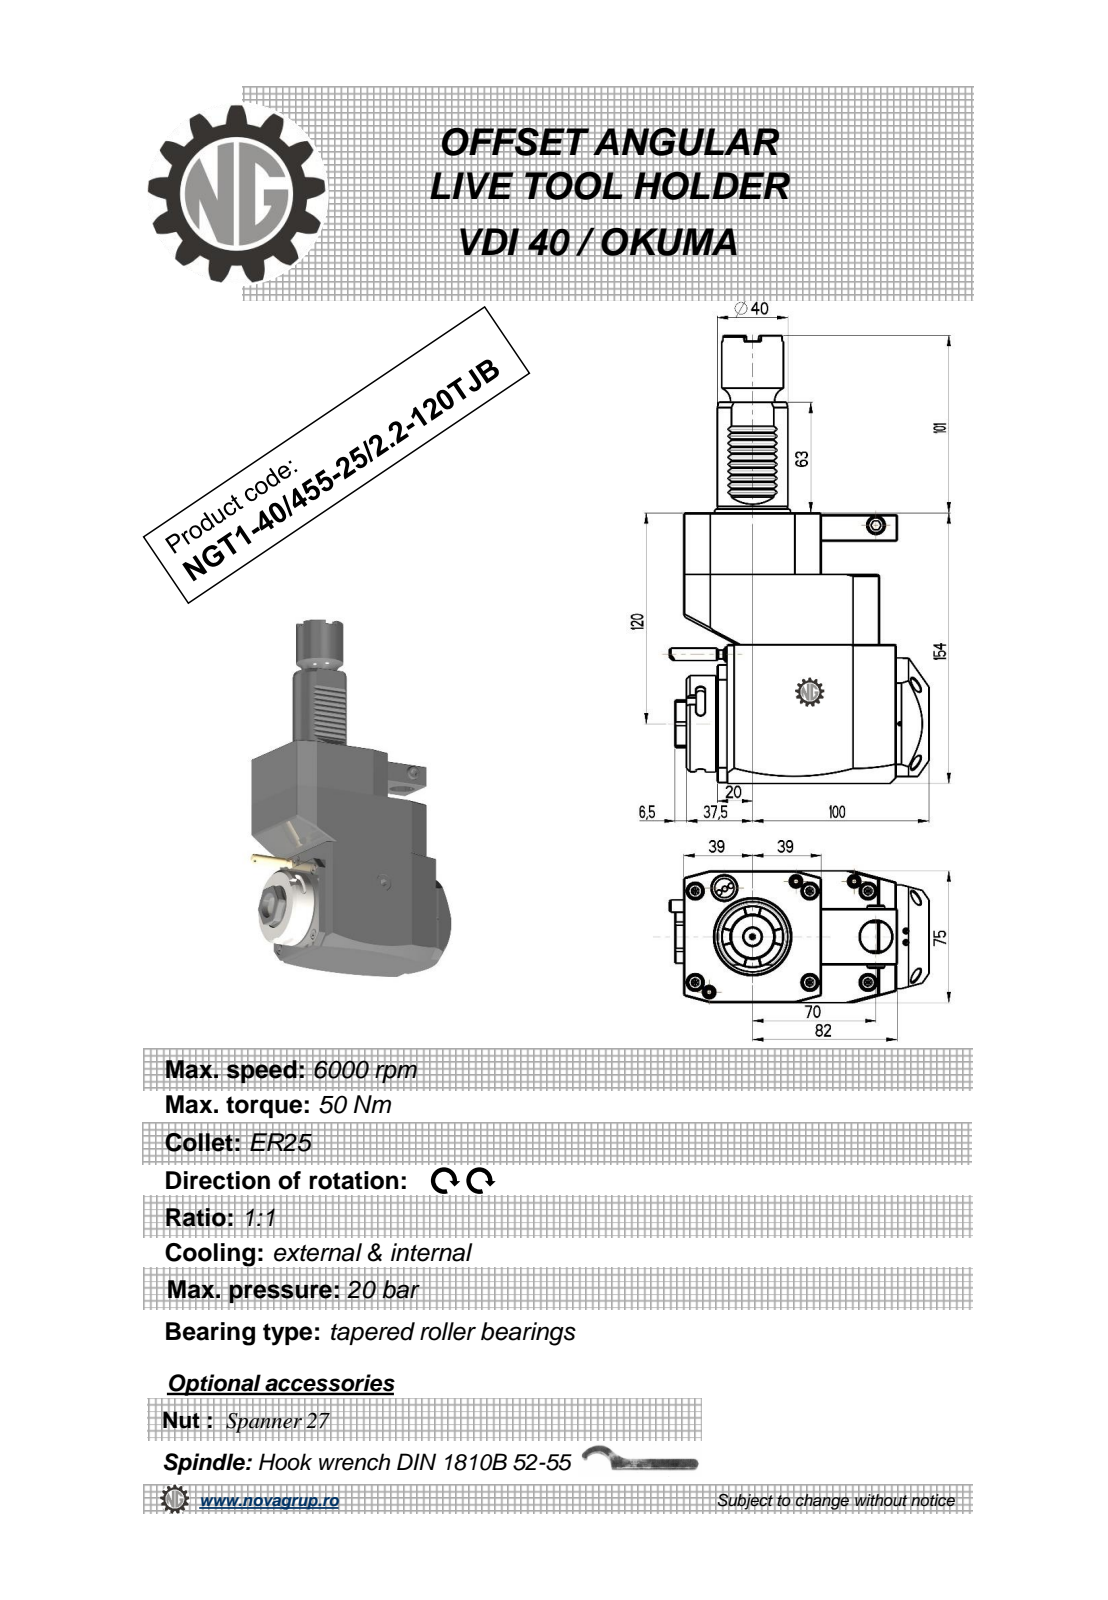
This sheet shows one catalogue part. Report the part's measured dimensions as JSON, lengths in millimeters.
{"part_name": "NGT1_40_455_25_1_2_120TJB", "step_written_by": "PRO/ENGINEER BY PARAMETRIC TECHNOLOGY CORPORATION, 2010280 (CONFIG_CONTROL_DESIGN)", "units": "millimeters", "bodies": {"solids": 1, "faces": 375, "planar": 199, "cylindrical": 70, "other": 106}, "overall_size": [255, 147.33, 75], "volume_mm3": 1305000, "surface_area_mm2": 94504, "round_holes": [[18, 2], [2.5, 1], [3, 1], [9.5, 1], [25, 1]], "round_bosses_or_shafts": [[8.96, 2], [55, 1], [48, 1], [40, 1], [35, 1], [10, 1], [7, 1], [5, 1]], "partial_cylinders_radius": [[0.3, 10], [2.5, 6], [180, 2], [0.5, 1], [4.25, 1], [15, 1], [24.5, 1], [37.5, 1]], "face_to_face_distances": [75, 154, 19, 119, 59, 111, 92, 35, 17.5, 53.5], "hole_center_spacings": [43.2, 70, 75.07, 112.5]}
